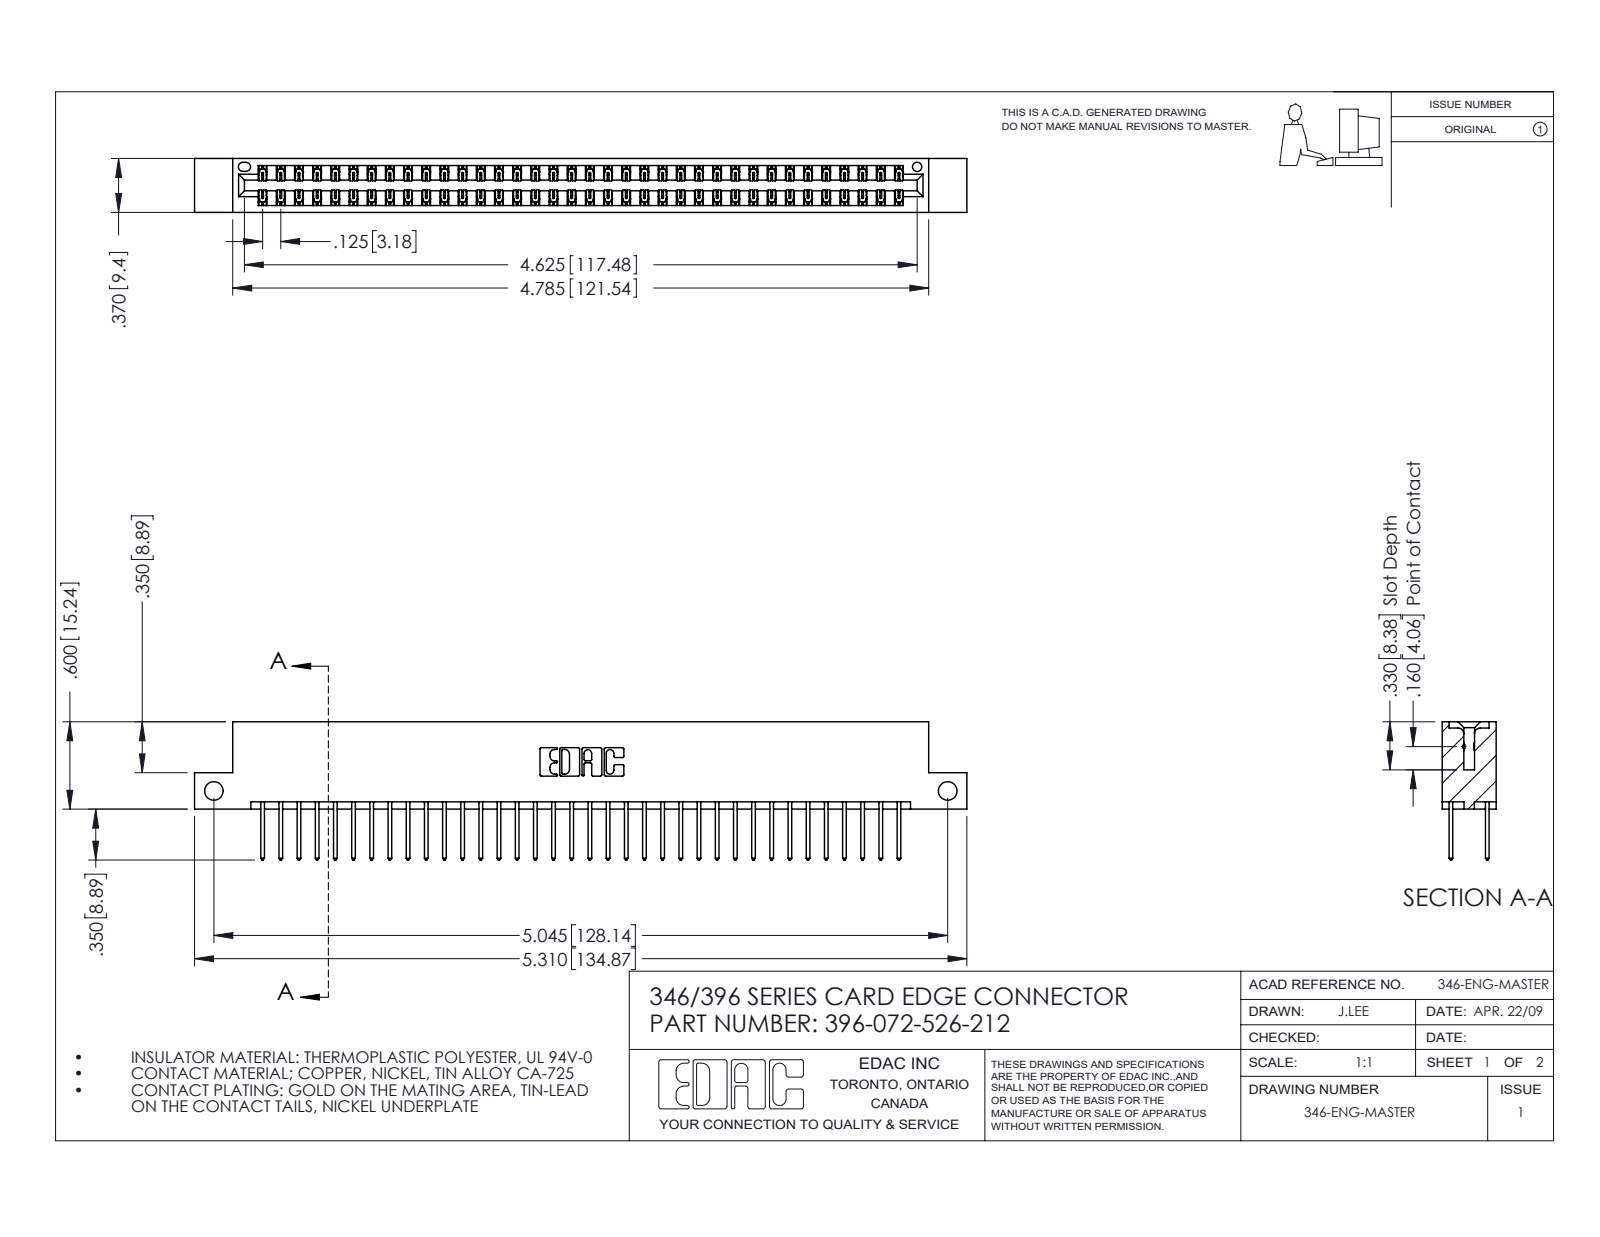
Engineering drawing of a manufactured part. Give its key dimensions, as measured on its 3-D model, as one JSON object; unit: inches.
{"part_name": "346 Part_Flush Mounting Lugs - Side Mount; 345-292-001_345-293-126; 396-072-526-212", "step_written_by": "SolidWorks 2016 (CONFIG_CONTROL_DESIGN)", "units": "inches", "bodies": {"solids": 73, "faces": 3866, "planar": 2596, "cylindrical": 1270, "other": 0}, "overall_size": [5.31, 0.95, 0.37], "volume_in3": 0.802, "surface_area_in2": 28.45, "round_holes": [[0.128, 2], [0.064, 1]], "partial_cylinders_radius": [[0.006, 108], [0.01, 72], [0.01, 22], [0.007, 6], [0.031, 6], [0.026, 3], [0.014, 2], [0.022, 2]], "face_to_face_distances": [0.048, 0.322, 0.25, 0.37, 0.072, 0.298, 0.025, 0.275, 0.148, 0.222], "hole_center_spacings": [5.045]}
